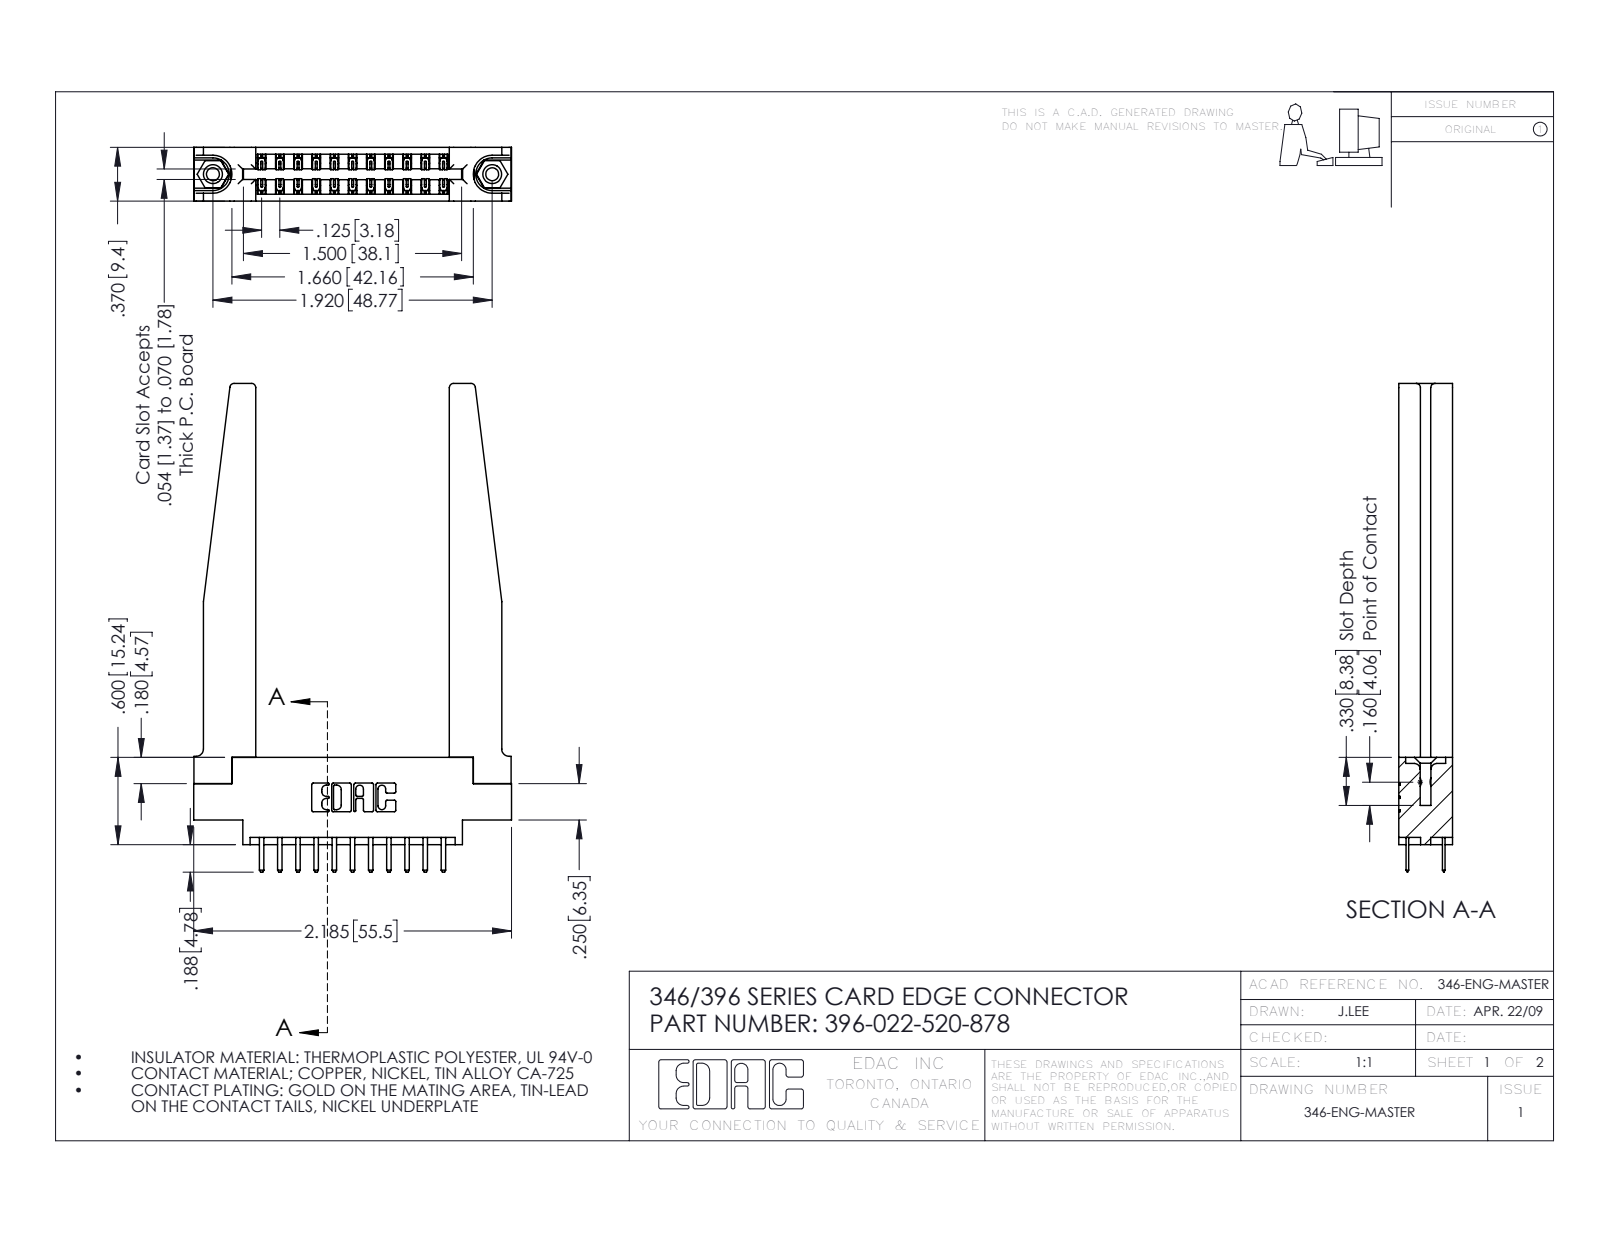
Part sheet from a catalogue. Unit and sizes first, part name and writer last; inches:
Units: inches
Overall size (bounding box): 3.358 × 2.185 × 0.37
Round holes (diameter × count): ⌀0.089 ×2, ⌀0.125 ×2, ⌀0.156 ×2, ⌀0.064 ×1
Round bosses / shafts (diameter × count): ⌀0.155 ×2
Partial cylindrical surfaces — rounded edges, fillets, slot ends (radius × count): R0.006 ×33, R0.01 ×26, R0.01 ×22, R0.03 ×8, R0.007 ×6, R0.031 ×6, R0.026 ×3, R0.014 ×2
Main face-to-face distances: 0.37, 0.15, 0.072, 0.148, 0.048, 0.322, 0.25, 0.102, 0.22, 0.173
Hole centre spacings: 0.246, 1.715, 1.92
Volume: 0.727 in³ · Surface area: 20.29 in²
Bodies: 27 solids, 1592 faces (1036 planar, 504 cylindrical, 52 other)
Part name (STEP PRODUCT): 346-220-078_345-220-078; 346 Part_0.170 Offset - 0.156 Dia-TH; 345-250-001_345-250-001-102; 345-292-001_345-293-120 (+1 more)
STEP written by: SolidWorks 2016 (CONFIG_CONTROL_DESIGN)
